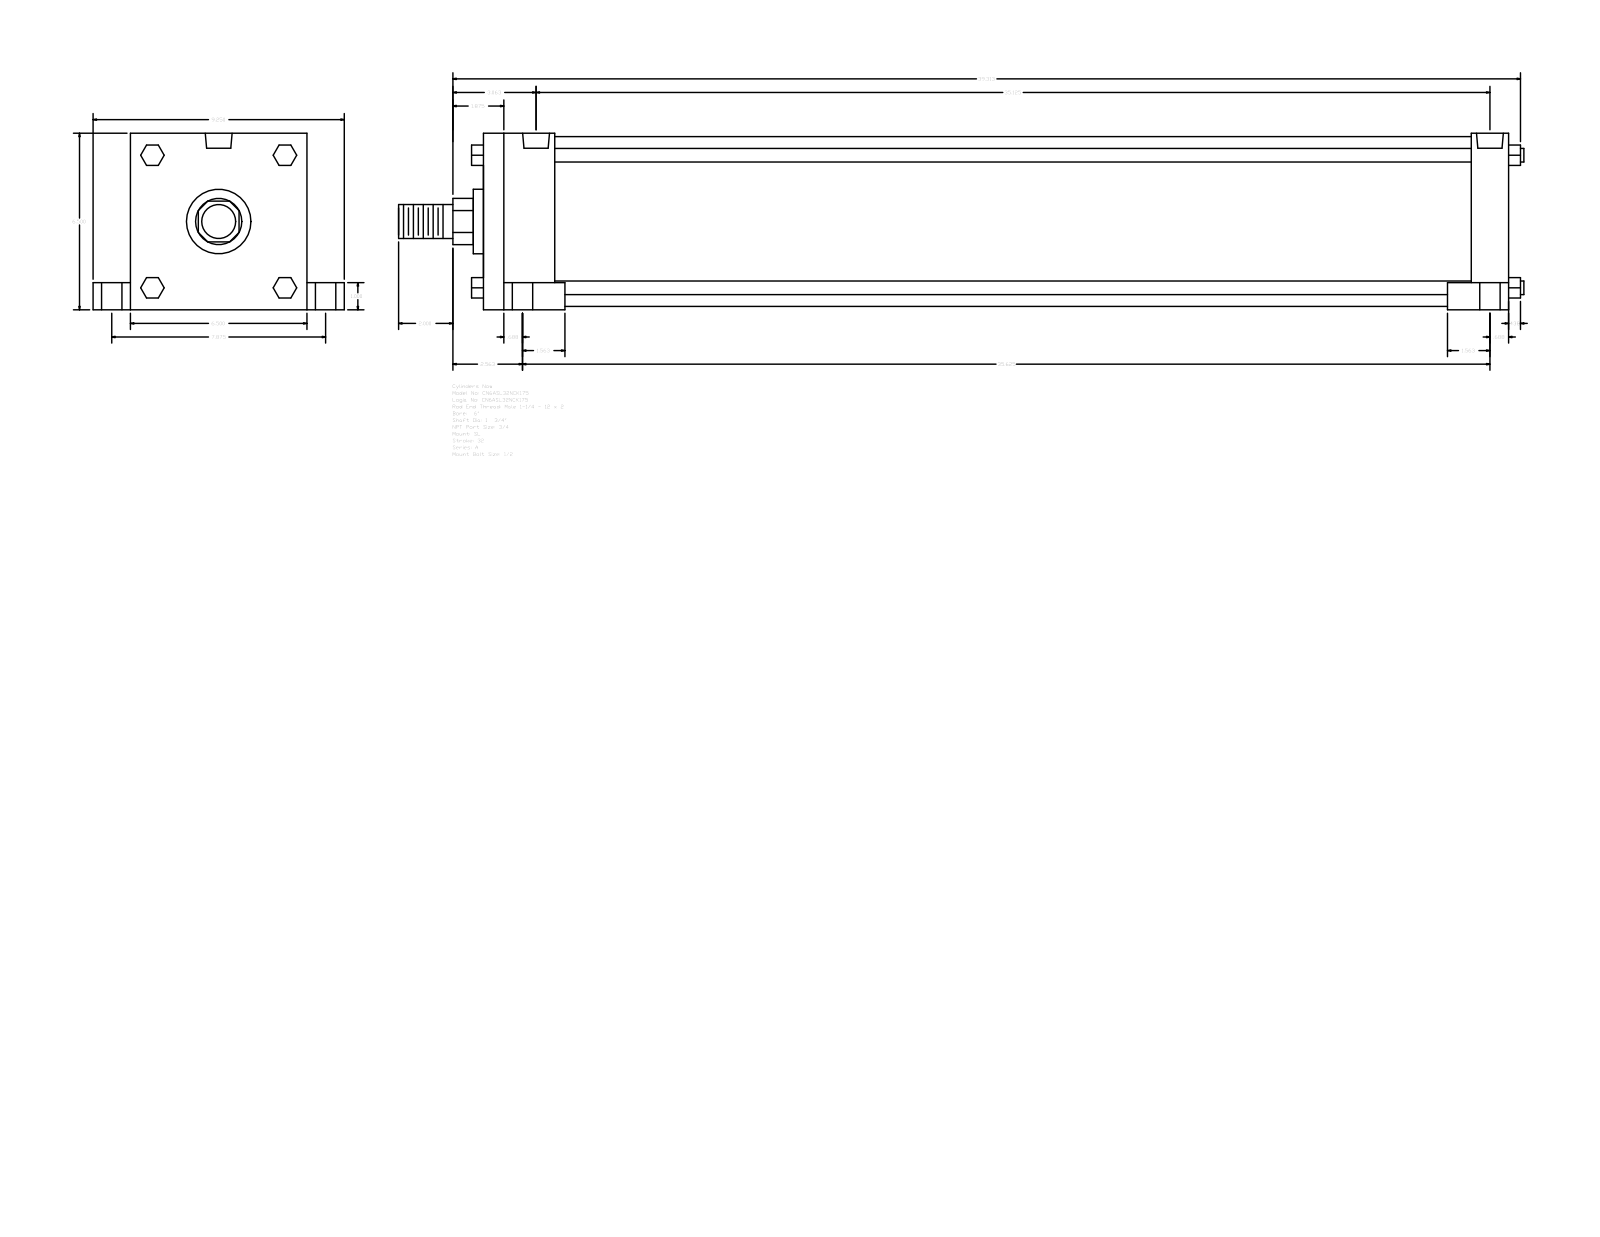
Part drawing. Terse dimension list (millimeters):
name: A_SL__0600_1.75
written by: GSSL Pune (CONFIG_CONTROL_DESIGN)
unit: mm
bodies: 0 solids, 150 faces (114 planar, 36 cylindrical, 0 other)
size: 1052.51 × 234.95 × 165.1
holes: 4× ⌀15.08, 4× ⌀19.05, 4× ⌀25.4, 2× ⌀25.12
bosses: 4× ⌀12.7, 1× ⌀158.75, 1× ⌀60.33, 1× ⌀44.45, 1× ⌀31.75
rounds: 1× R21.63
face distances: 165.1, 958.85, 34.92, 66.68, 892.17, 923.93, 857.25, 25.4, 139.7, 200.02
hole spacings: 5.56, 100.01, 100.16, 100.81, 101.66, 200.02, 881.05, 886.61
